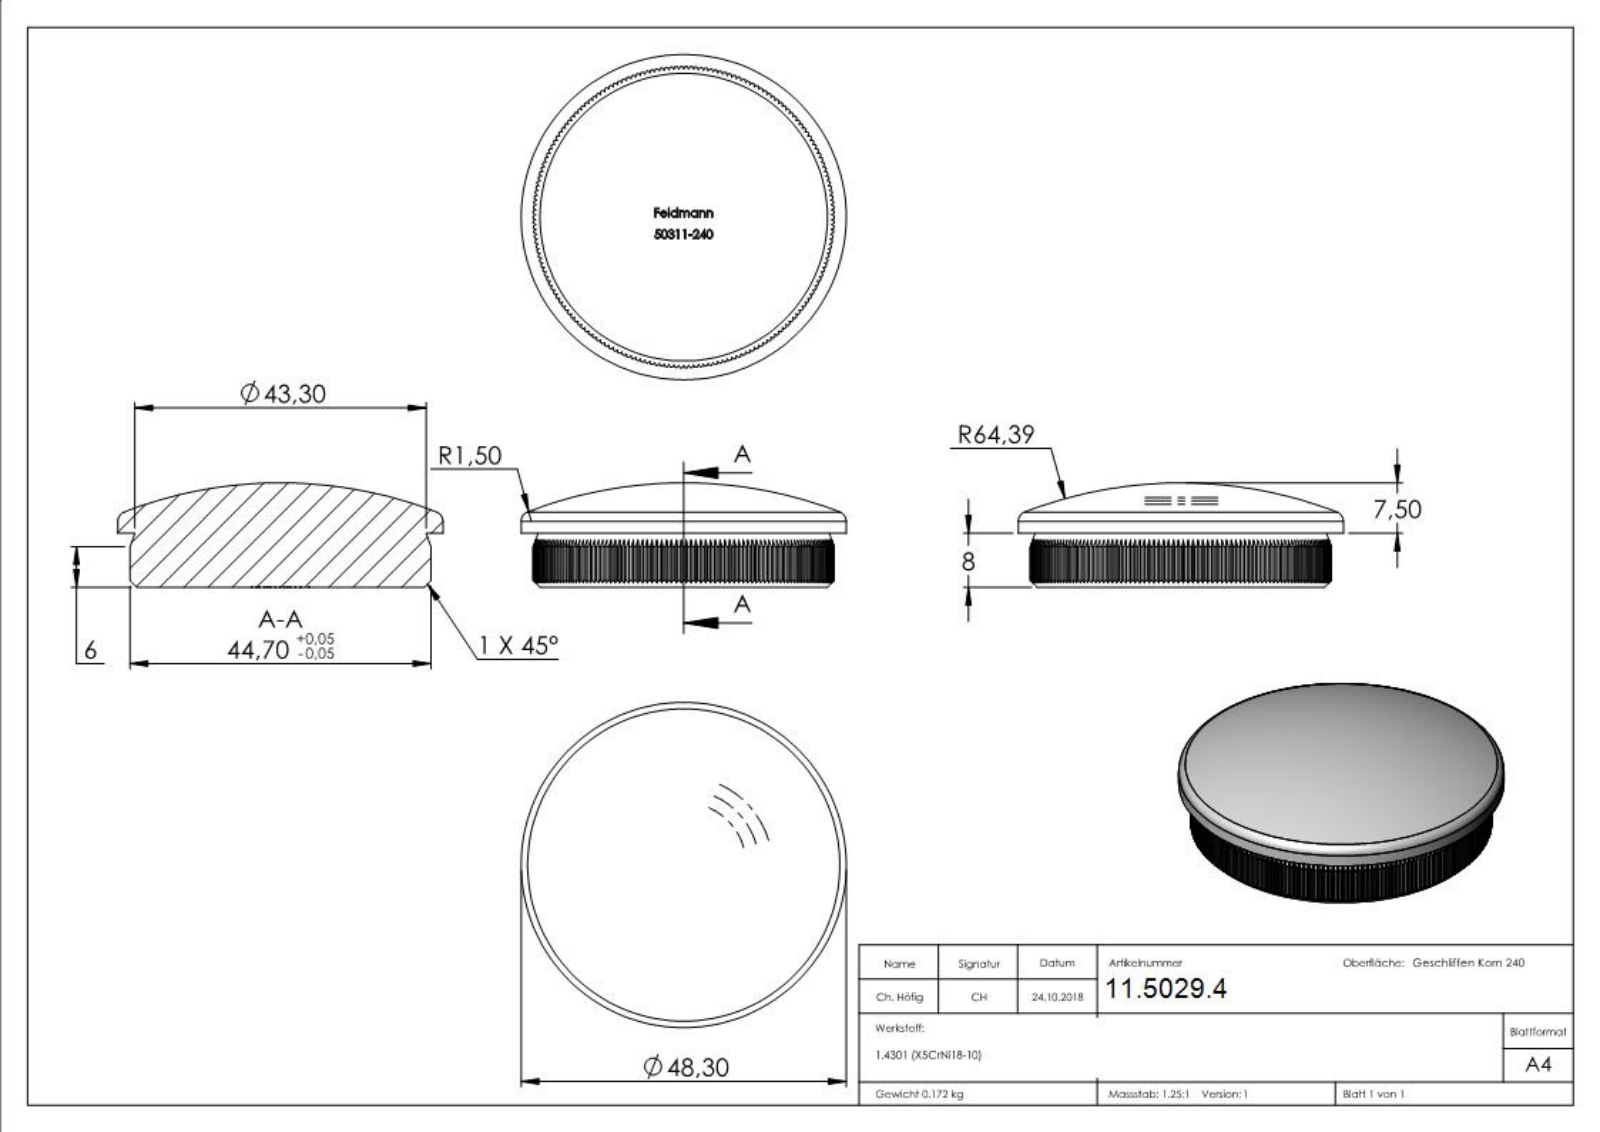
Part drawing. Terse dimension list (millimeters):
name: 50311-240
written by: SolidWorks 2015 (CONFIG_CONTROL_DESIGN)
unit: mm
bodies: 1 solid, 804 faces (501 planar, 192 cylindrical, 111 other)
size: 48.3 × 48.3 × 15.5
volume: 21 776 mm³; area: 5 705 mm²
bosses: 1× ⌀48.3
rounds: 1× R22.35
face distances: 8, 22, 21.98, 22.02, 7.9, 2.97, 0.39, 1.4, 3.39, 3.19
